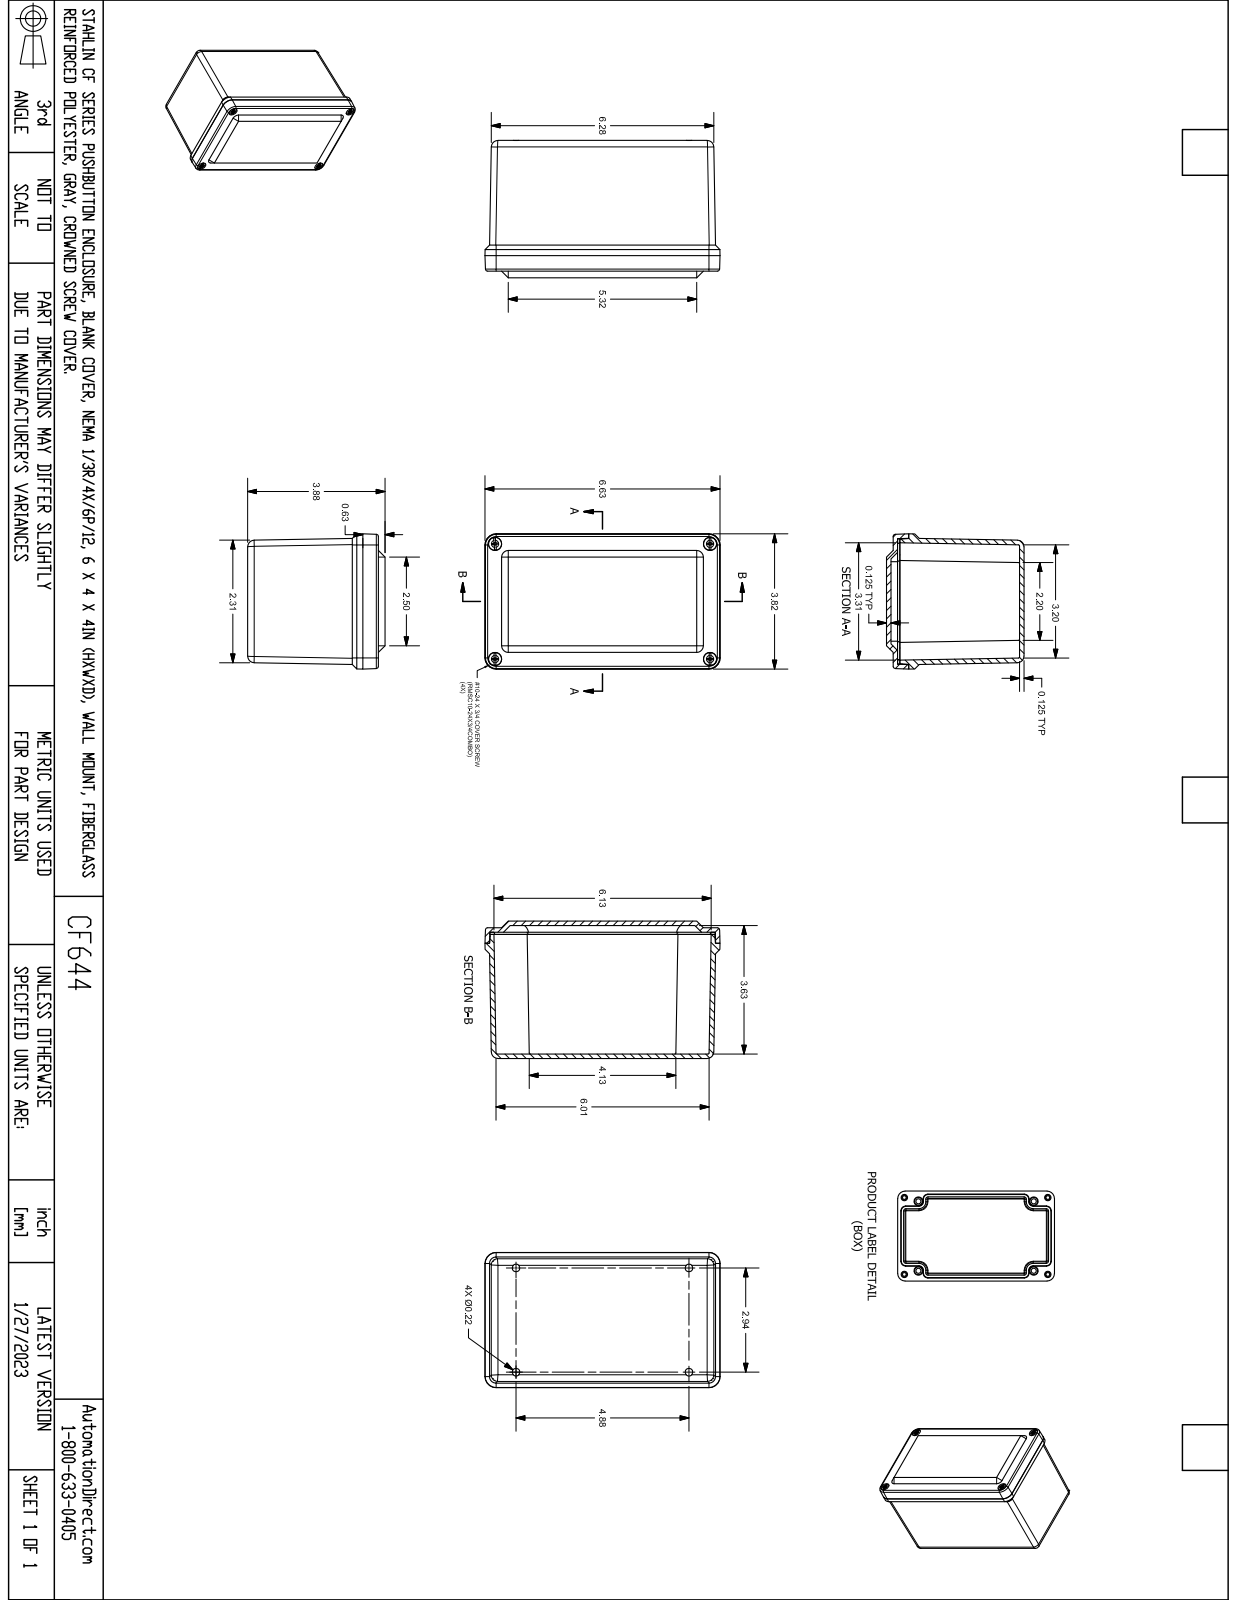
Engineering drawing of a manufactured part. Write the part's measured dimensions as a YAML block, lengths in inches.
part_name: "CO644"
step_written_by: "SolidWorks 2018 (AUTOMOTIVE_DESIGN)"
units: inches
bodies: {solids: 11, faces: 379, planar: 183, cylindrical: 100, other: 96}
overall_size: [6.625, 3.875, 3.812]
volume: 20.35
surface_area: 267.7
round_holes:
  - {diameter: 0.219, count: 8}
  - {diameter: 0.159, count: 4}
  - {diameter: 0.19, count: 4}
  - {diameter: 0.375, count: 4}
round_bosses_or_shafts:
  - {diameter: 0.371, count: 4}
  - {diameter: 0.27, count: 4}
  - {diameter: 0.177, count: 4}
partial_cylinders:
  - {radius: 0.031, count: 20}
  - {radius: 0.012, count: 16}
  - {radius: 0.176, count: 4}
  - {radius: 0.22, count: 4}
  - {radius: 0.313, count: 4}
  - {radius: 0.325, count: 4}
  - {radius: 0.062, count: 2}
  - {radius: 0.063, count: 2}
face_to_face_distances: [0.125, 0.131, 3.75, 0.187, 3.563, 0.5, 3.875, 3.625, 0.063, 3.438]
hole_center_spacings: [0.614, 3.15, 5.471, 6.283, 2.938, 3.25, 4.875, 5.692]
